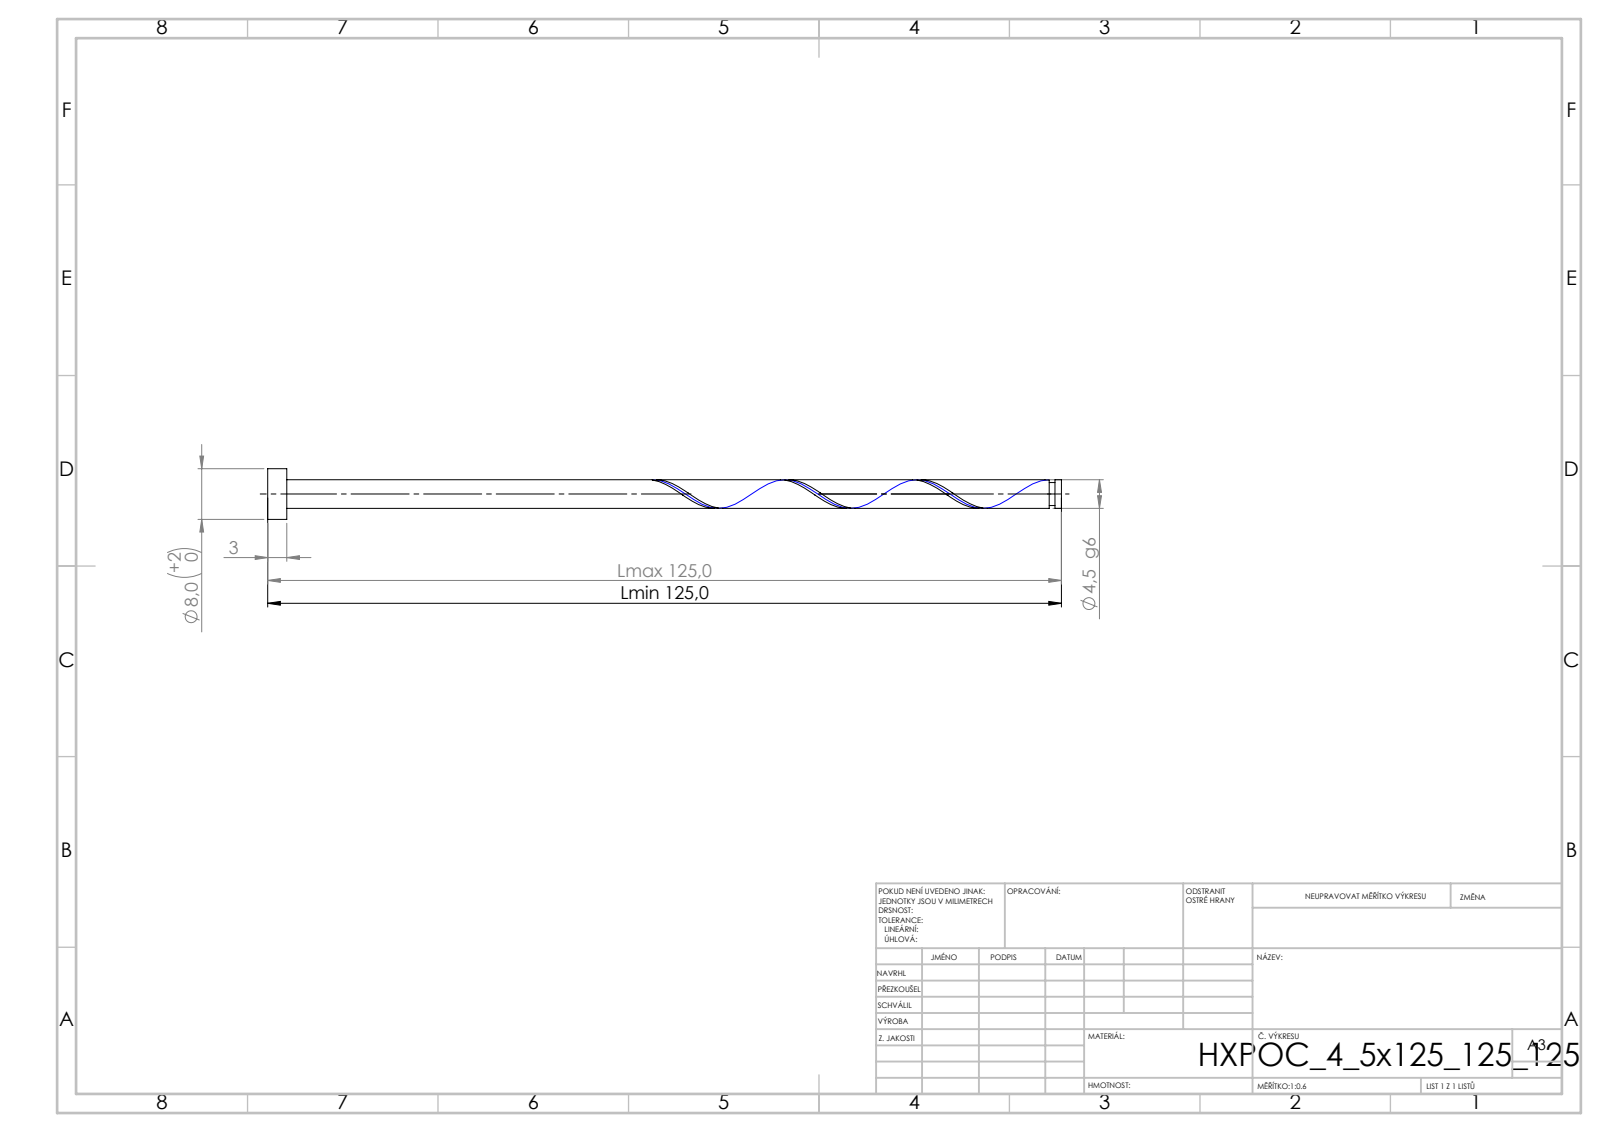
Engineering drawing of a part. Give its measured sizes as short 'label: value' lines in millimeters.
written by: SolidWorks 2019 (CONFIG_CONTROL_DESIGN)
unit: mm
bodies: 1 solid, 21 faces (6 planar, 14 cylindrical, 1 other)
size: 125 × 8 × 8
volume: 2 067 mm³; area: 1 944 mm²
bosses: 1× ⌀8, 1× ⌀4.5, 1× ⌀3.6
face distances: 3, 125, 122, 123.98, 120.98, 1.02, 123.08, 120.08, 0.9, 1.92
